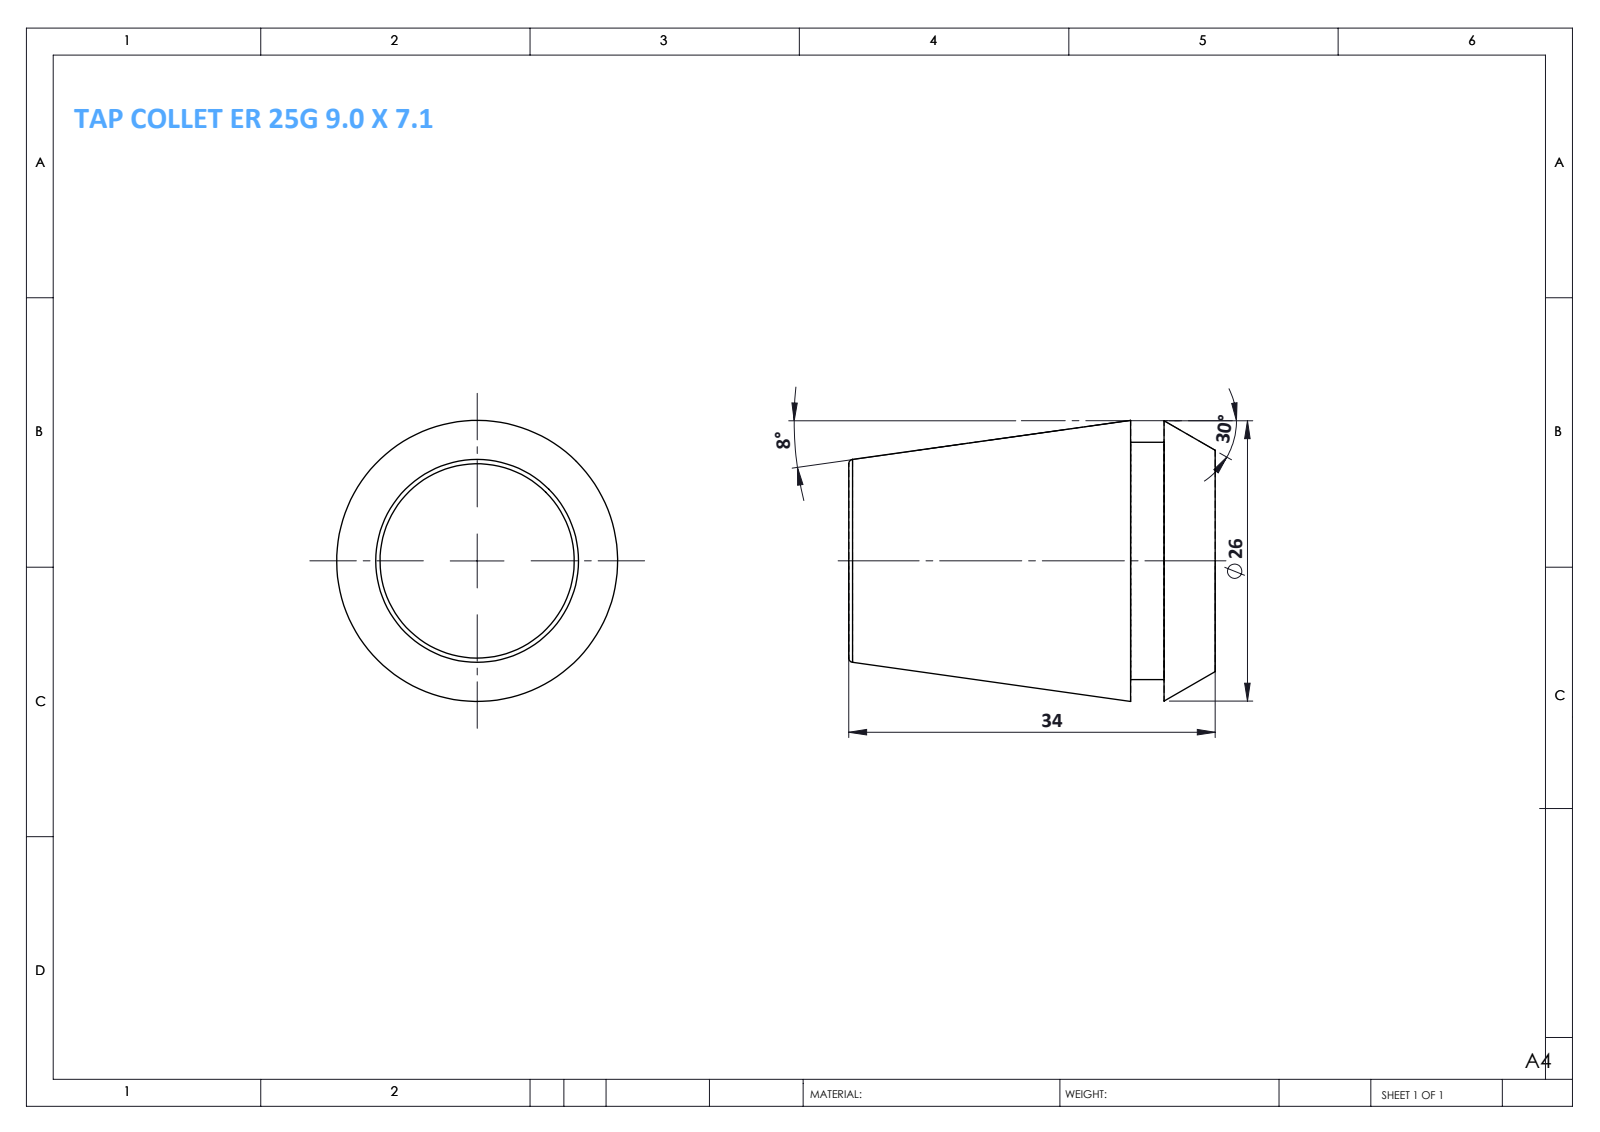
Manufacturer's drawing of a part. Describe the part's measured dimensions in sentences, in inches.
The part is named "TAP COLLET ER 25G 9.0 X 7.1". Its 3-D file was written by "SolidWorks 2014 (CONFIG_CONTROL_DESIGN)". It is 1 solid with 12 faces: 4 planar, 2 cylindrical and 6 other. Overall it measures 1.339 by 1.026 by 1.026 inches. Its volume is 0.83 cubic inches and its surface area 5.233 square inches. Round bosses or shafts: 1 of diameter 0.866. The main face-to-face distances are 1.339, 0.309, 1.03, 0.187, 0.122, 1.152.
